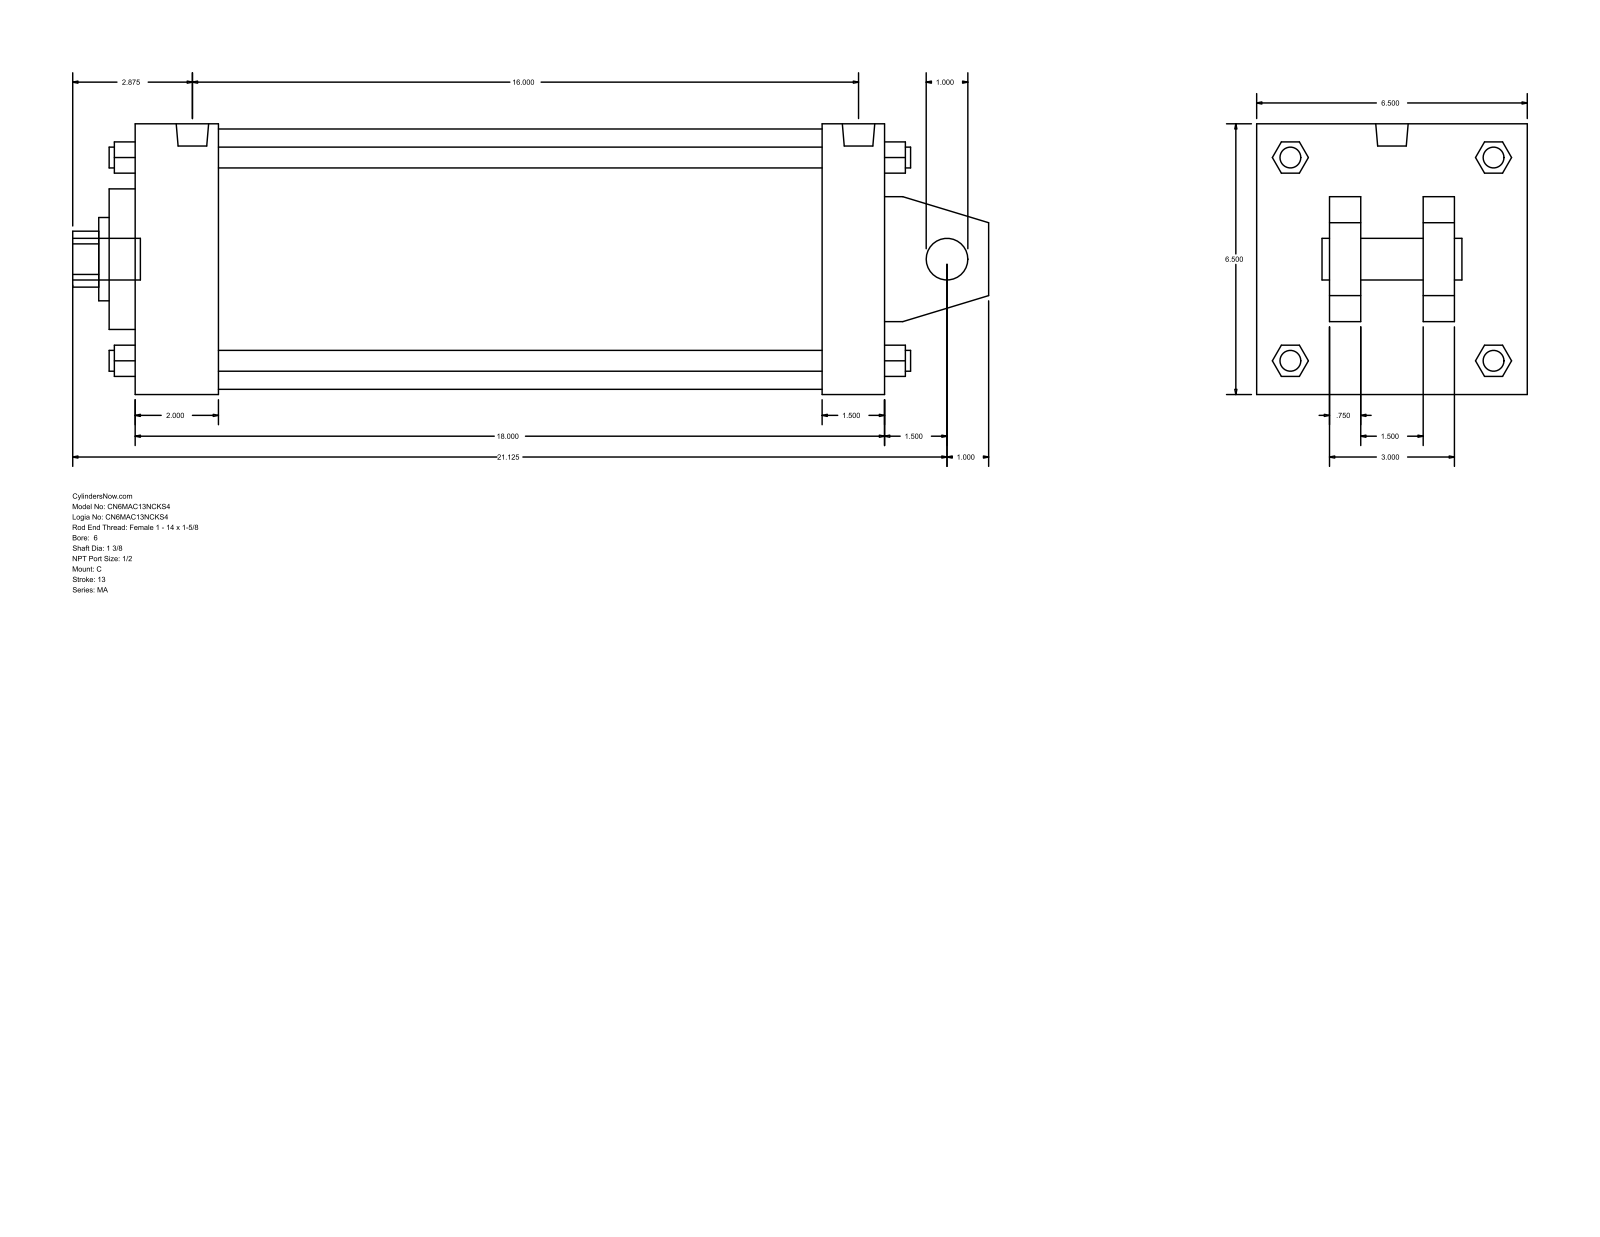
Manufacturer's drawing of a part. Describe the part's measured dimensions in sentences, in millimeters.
The part is named "MA_C__0600_1.375". Its 3-D file was written by "GSSL Pune (CONFIG_CONTROL_DESIGN)". It is 0 solids with 141 faces: 109 planar, 32 cylindrical and 0 other. Overall it measures 558.8 by 165.1 by 165.1 millimeters. Round holes: 1 of diameter 25.4, 1 of diameter 34.92, 1 of diameter 50.8, 1 of diameter 85.72, 1 of diameter 158.75. Round bosses or shafts: 4 of diameter 17.46, 4 of diameter 12.7, 2 of diameter 19.77, 1 of diameter 25.4. Partial cylindrical surfaces (rounded edges, fillets, slot ends): 1 of radius 17.06. The main face-to-face distances are 165.1, 457.2, 38.1, 19.05, 63.5, 101.6, 50.8, 44.45, 120.65, 419.1.
